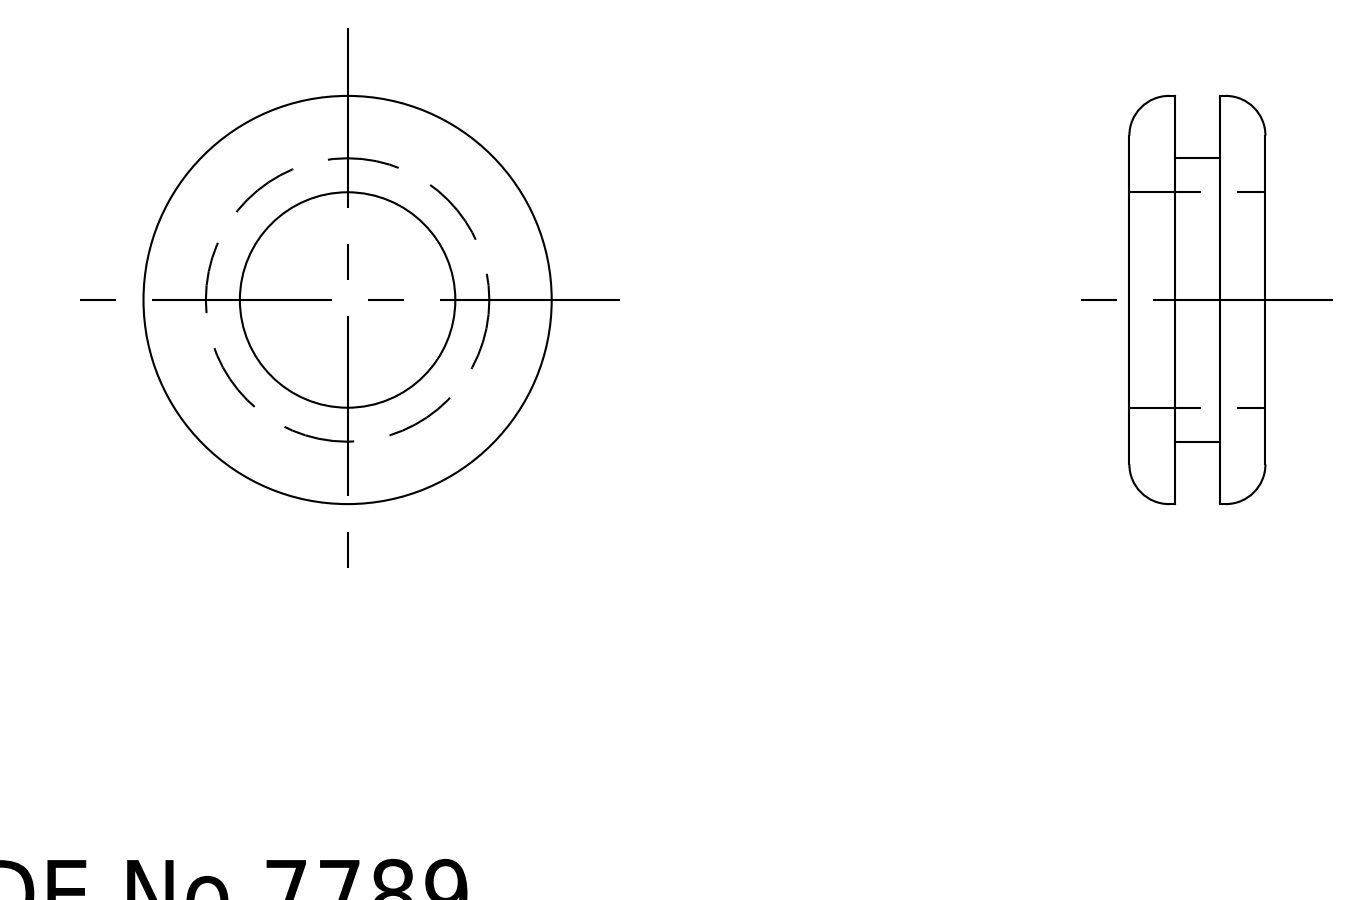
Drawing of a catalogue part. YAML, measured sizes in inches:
part_name: "TM_346_4"
step_written_by: "SolidWorks 2015 (AUTOMOTIVE_DESIGN)"
units: inches
bodies: {solids: 1, faces: 16, planar: 4, cylindrical: 8, other: 4}
overall_size: [0.709, 0.709, 0.236]
volume: 0.047
surface_area: 1.592
round_holes:
  - {diameter: 0.374, count: 1}
round_bosses_or_shafts:
  - {diameter: 0.709, count: 1}
  - {diameter: 0.492, count: 1}
face_to_face_distances: [0.079, 0.157, 0.236]
